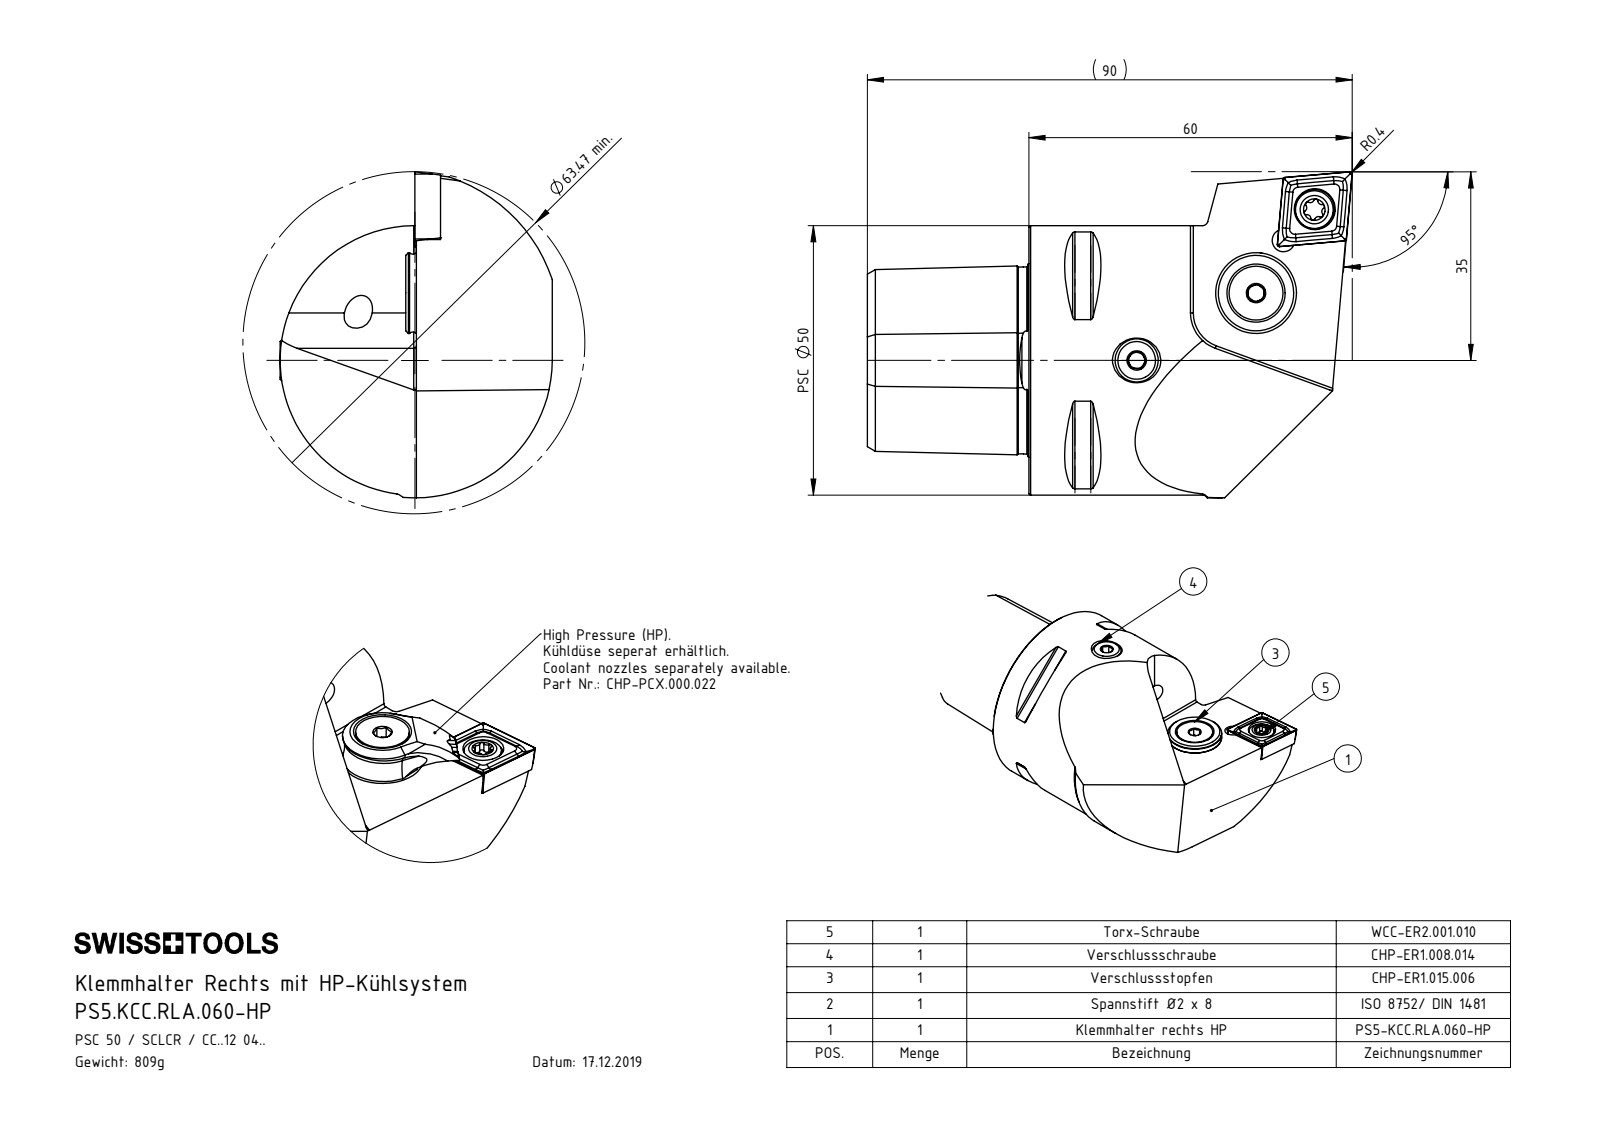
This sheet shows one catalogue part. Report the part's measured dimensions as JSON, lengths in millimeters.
{"part_name": "WCC-ER2.001.010_A; DIN 7991 - M5x15; ISO 8752 2x8; PS5.KCC.RLA.060-HP (+6 more)", "step_written_by": "SolidWorks 2017 (AUTOMOTIVE_DESIGN)", "units": "millimeters", "bodies": {"solids": 8, "faces": 377, "planar": 88, "cylindrical": 103, "other": 186}, "overall_size": [90, 60.5, 50.5], "volume_mm3": 103358, "surface_area_mm2": 22748, "round_holes": [[4.2, 4], [5, 2], [1.2, 1], [2, 1], [2.5, 1], [3, 1], [4, 1], [5.2, 1], [5.5, 1], [6.1, 1], [7, 1], [7.6, 1]], "round_bosses_or_shafts": [[5, 2], [50, 1], [15, 1], [13.4, 1], [10, 1], [8, 1], [7, 1], [5.5, 1]], "partial_cylinders_radius": [[0.5, 10], [0.39, 6], [0.69, 3], [0.69, 3], [4, 1], [7, 1], [25.5, 1], [30, 1]], "face_to_face_distances": [30, 25.2, 60, 20.7, 4.5, 20.74, 4.46, 19.18, 44.4, 20], "hole_center_spacings": [4.5, 7.35, 8, 8.09, 8.2, 11.01, 15.44, 15.55]}
